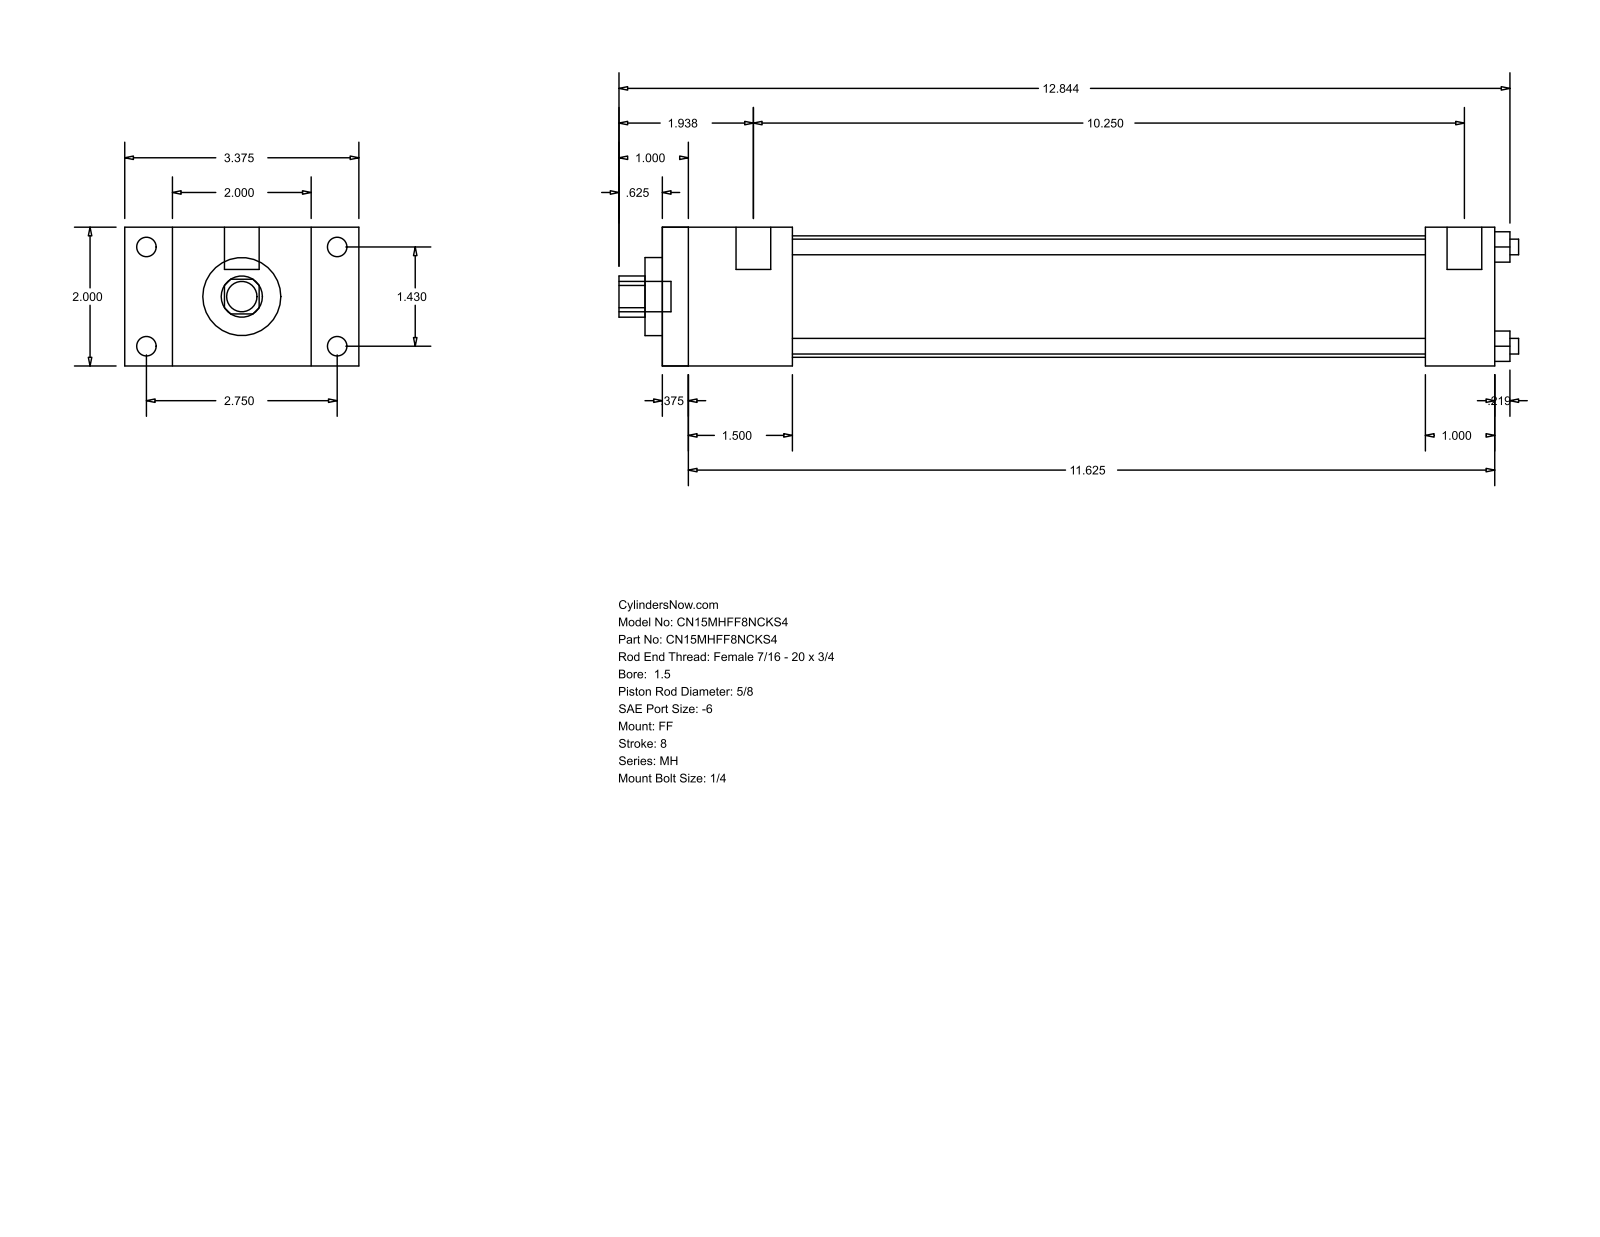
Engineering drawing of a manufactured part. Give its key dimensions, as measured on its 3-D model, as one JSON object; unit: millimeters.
{"part_name": "MH_FF__0150_0.625", "step_written_by": "GSSL Pune (CONFIG_CONTROL_DESIGN)", "units": "millimeters", "bodies": {"solids": 0, "faces": 92, "planar": 64, "cylindrical": 28, "other": 0}, "overall_size": [329.41, 85.72, 50.8], "round_holes": [[5.71, 4], [15.88, 1], [28.57, 1], [44.45, 1]], "round_bosses_or_shafts": [[7.14, 4], [5.56, 4], [12.7, 2], [11.11, 1]], "partial_cylinders_radius": [[7.54, 1]], "face_to_face_distances": [50.8, 304.8, 9.52, 295.28, 17.46, 68.26, 47.62, 38.1, 257.18, 279.39], "hole_center_spacings": [25.68, 36.32, 51.36]}
